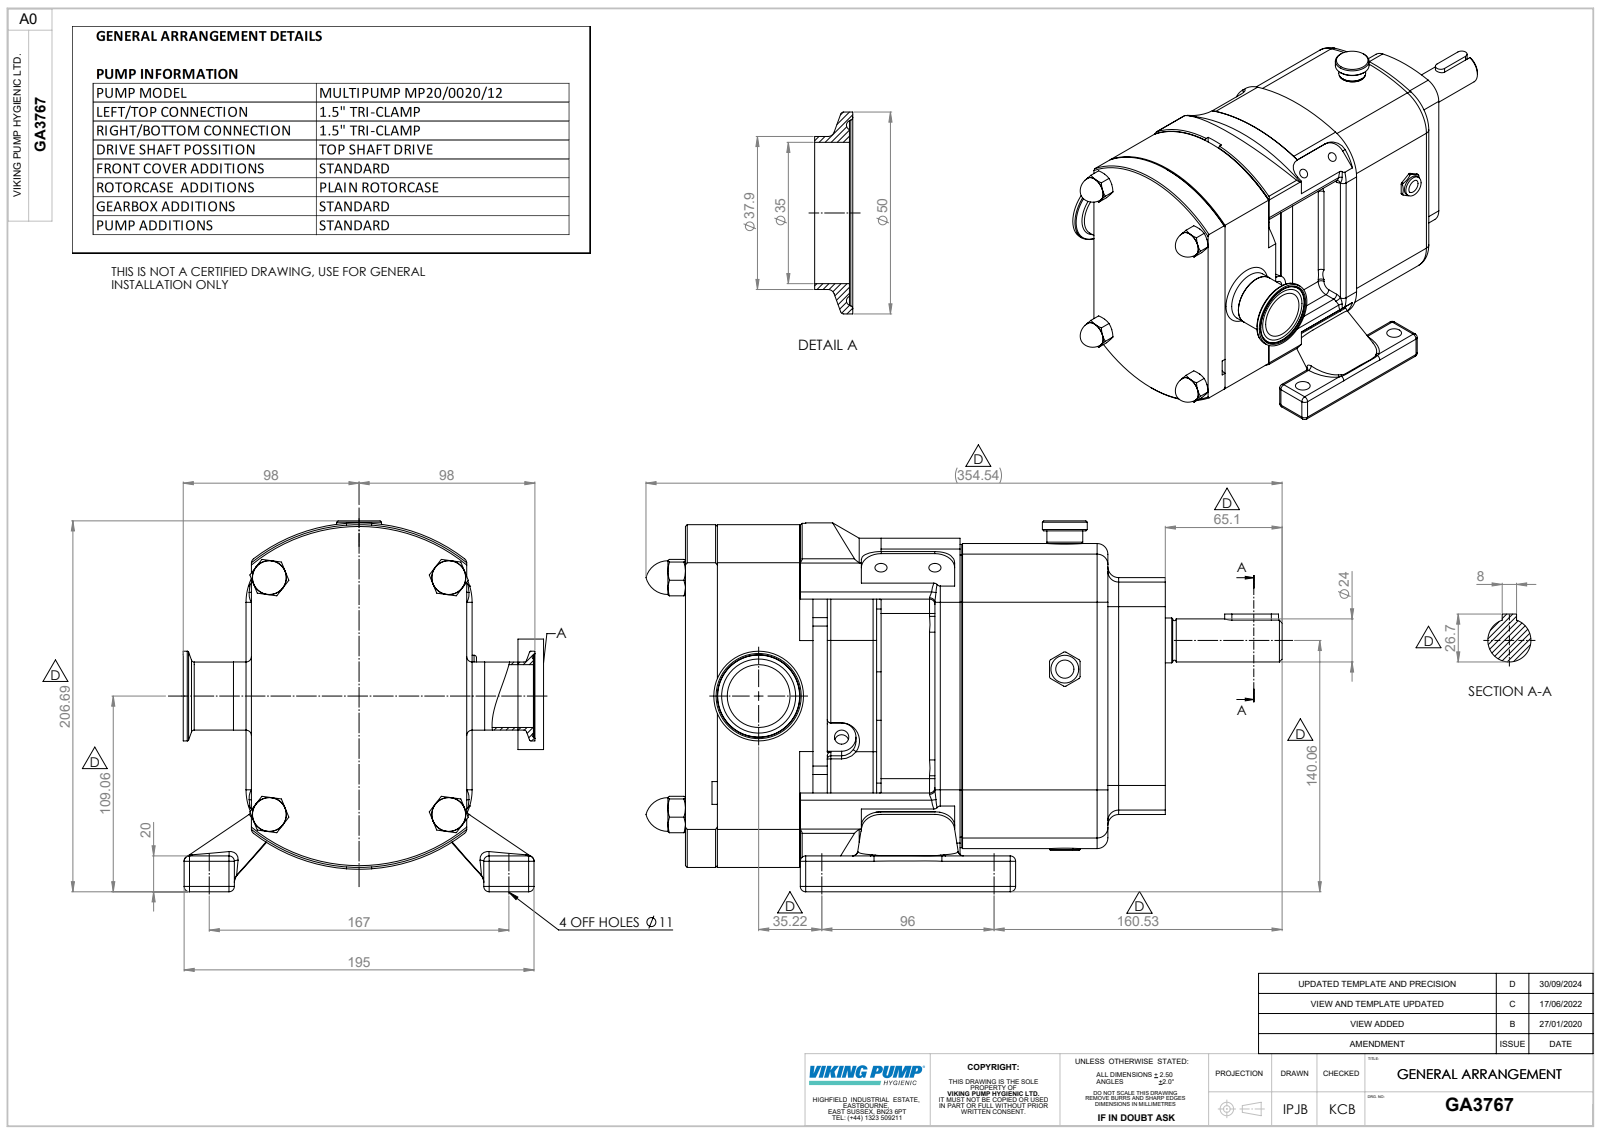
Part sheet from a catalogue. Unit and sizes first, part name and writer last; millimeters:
Units: millimetres
Overall size (bounding box): 354.54 × 206.69 × 196
Round holes (diameter × count): ⌀6.8 ×4, ⌀11 ×4, ⌀6.47 ×3, ⌀8 ×2, ⌀22.53 ×1, ⌀35 ×1
Round bosses / shafts (diameter × count): ⌀35 ×2, ⌀17 ×2, ⌀50 ×1, ⌀38 ×1, ⌀37.9 ×1, ⌀25.02 ×1, ⌀25 ×1, ⌀24 ×1
Partial cylindrical surfaces — rounded edges, fillets, slot ends (radius × count): R3 ×52, R2 ×18, R1 ×12, R6 ×8, R11.1 ×8, R1.27 ×6, R4 ×6, R8 ×6
Main face-to-face distances: 120, 109.04, 158.4, 267.44, 25, 95, 32, 126.4, 235.44, 160.89
Hole centre spacings: 30.05, 53.69, 96, 167.01, 192.64, 53.7, 61.08, 92.34
Volume: 4 756 000 mm³ · Surface area: 297 945 mm²
Bodies: 3 solids, 827 faces (253 planar, 284 cylindrical, 290 other)
Part name (STEP PRODUCT): Copy of CP20-0020-12 H T^GA3767; Copy of Z94-5121-22 - 1.5 INCH^GA3767; GA3767
STEP written by: SolidWorks 2023 (AUTOMOTIVE_DESIGN)
